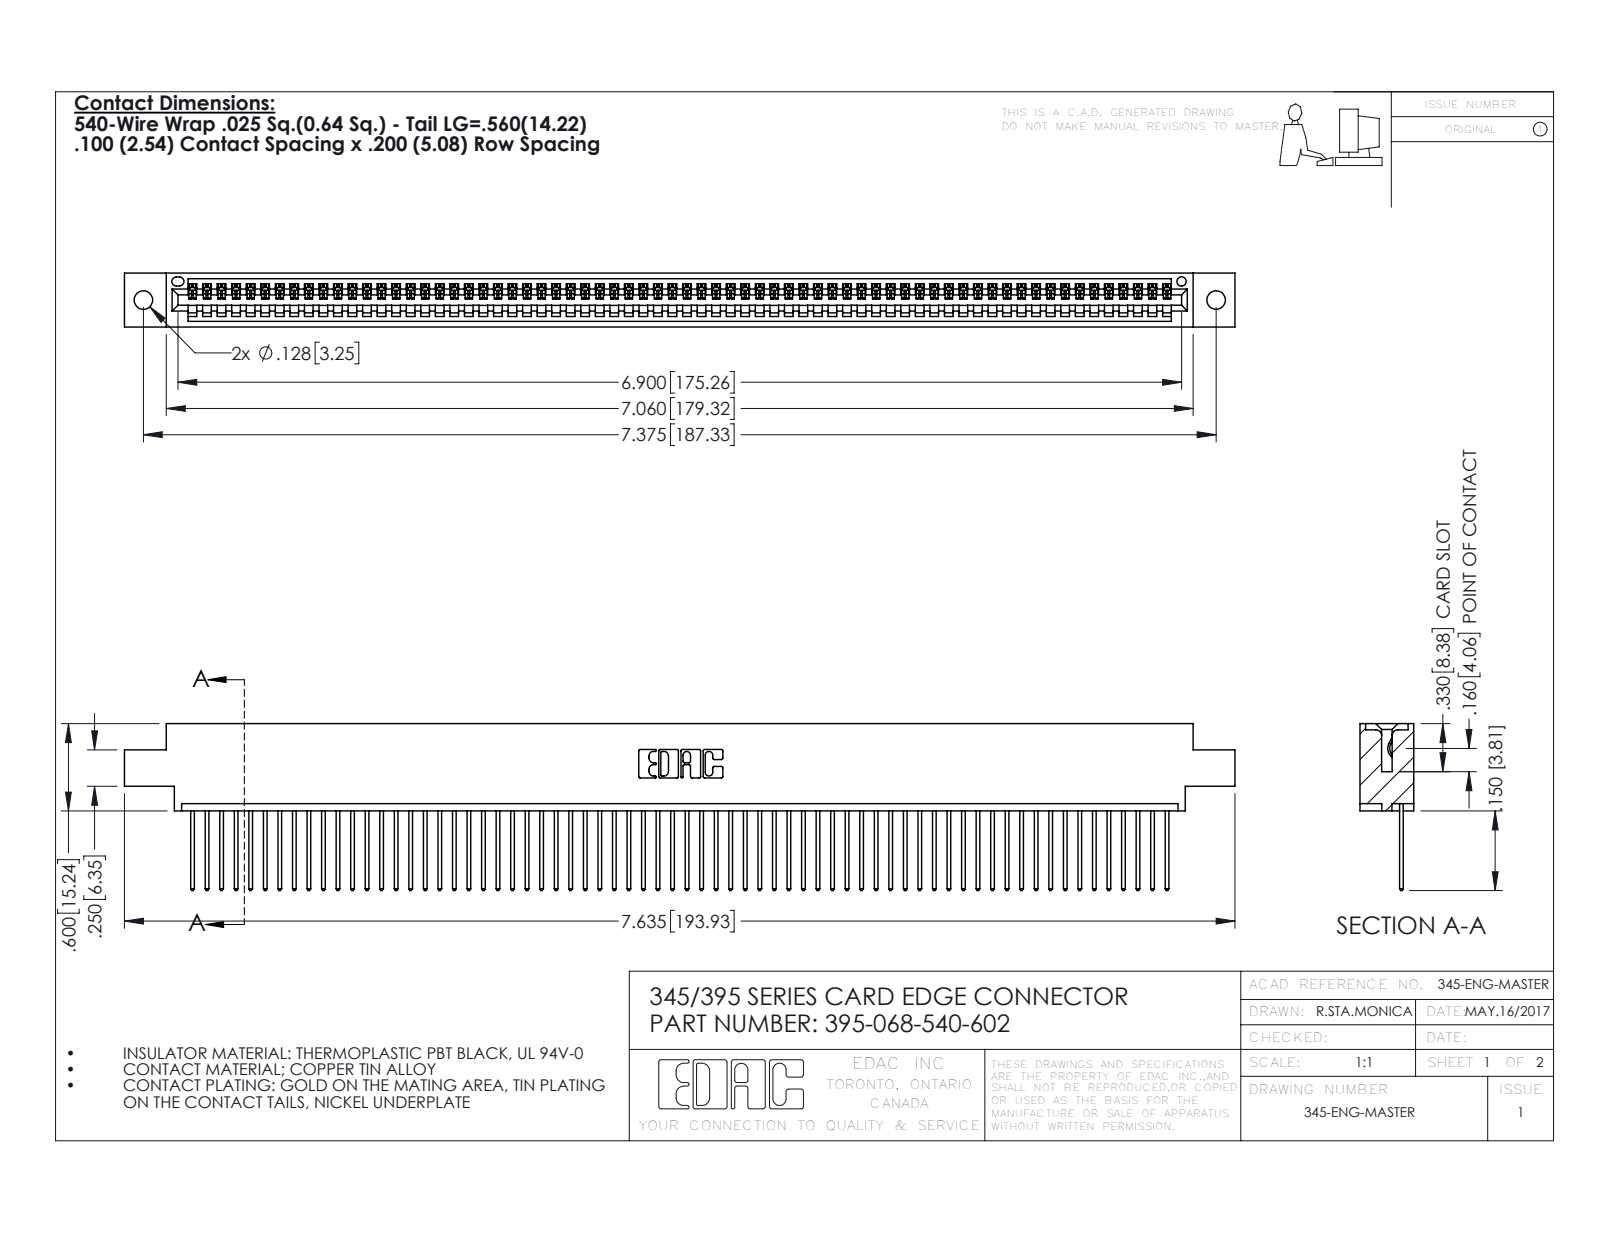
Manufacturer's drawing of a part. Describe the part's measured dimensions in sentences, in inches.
The part is named "345 Part_0.170 Offset - 0.128 Dia; 395-068-540-602; 345-292-001_345-293-140". Its 3-D file was written by "SolidWorks 2016 (CONFIG_CONTROL_DESIGN)". It is 69 solids with 4074 faces: 2804 planar, 1270 cylindrical and 0 other. Overall it measures 7.635 by 1.147 by 0.37 inches. Its volume is 1.133 cubic inches and its surface area 39.61 square inches. Round holes: 2 of diameter 0.128, 1 of diameter 0.064. Partial cylindrical surfaces (rounded edges, fillets, slot ends): 136 of radius 0.006, 136 of radius 0.01, 22 of radius 0.01, 6 of radius 0.007, 6 of radius 0.031, 3 of radius 0.026, 2 of radius 0.031, 2 of radius 0.04. The main face-to-face distances are 0.072, 0.298, 0.37, 0.098, 0.272, 0.025, 0.2, 0.225, 0.175, 0.149. The hole center spacings are 0.27, 7.139, 7.375.
